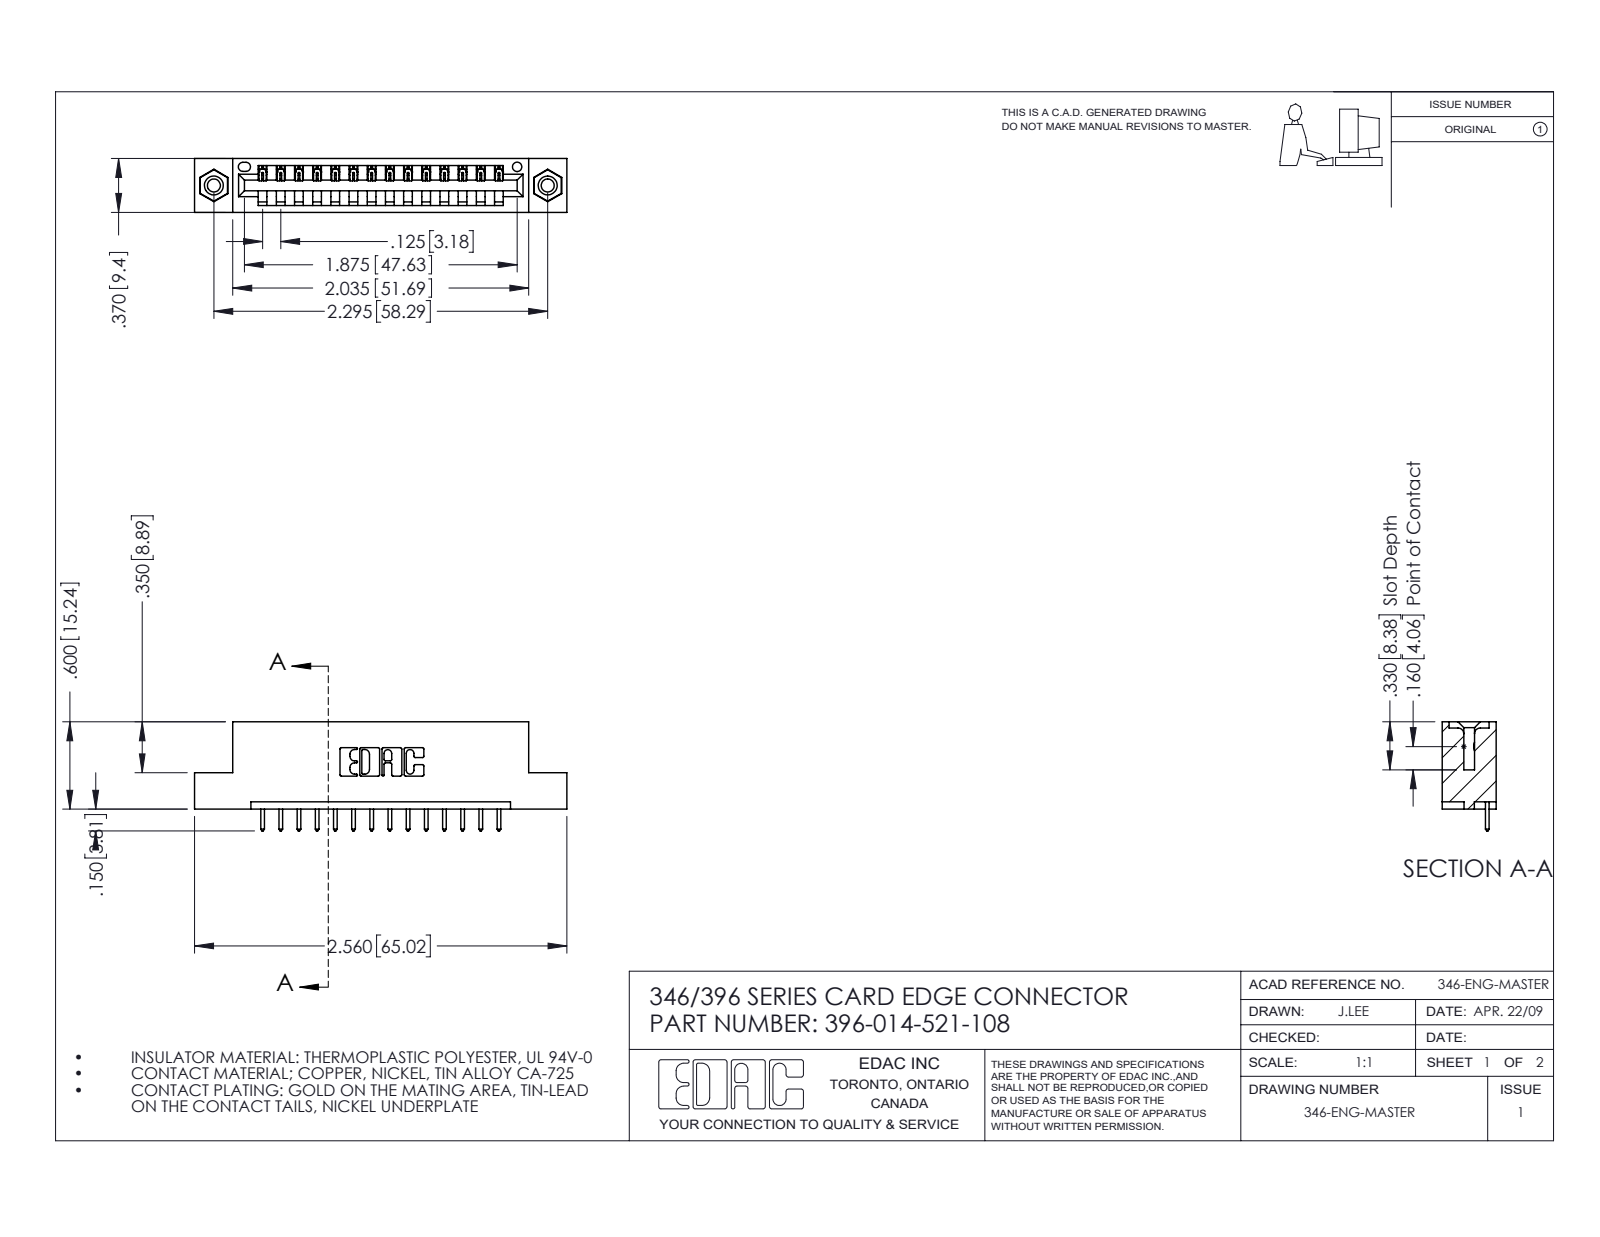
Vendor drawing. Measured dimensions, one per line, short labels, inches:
name: 345-292-001_345-293-121; 346 Part_Flush Mounting Lugs - 0.156 Dia-TI; 345-250-001_345-250-003-102; 396-014-521-108
written by: SolidWorks 2016 (CONFIG_CONTROL_DESIGN)
unit: in
bodies: 17 solids, 994 faces (668 planar, 310 cylindrical, 16 other)
size: 2.56 × 0.75 × 0.37
volume: 0.365 in³; area: 10.91 in²
holes: 2× ⌀0.089, 2× ⌀0.125, 2× ⌀0.156, 1× ⌀0.064
bosses: 2× ⌀0.155
rounds: 28× R0.006, 28× R0.01, 22× R0.01, 6× R0.007, 6× R0.031, 3× R0.026, 2× R0.031, 2× R0.04
face distances: 0.25, 0.048, 0.322, 0.37, 0.072, 0.298, 0.025, 0.148, 0.222, 0.1
hole spacings: 0.246, 2.089, 2.295
